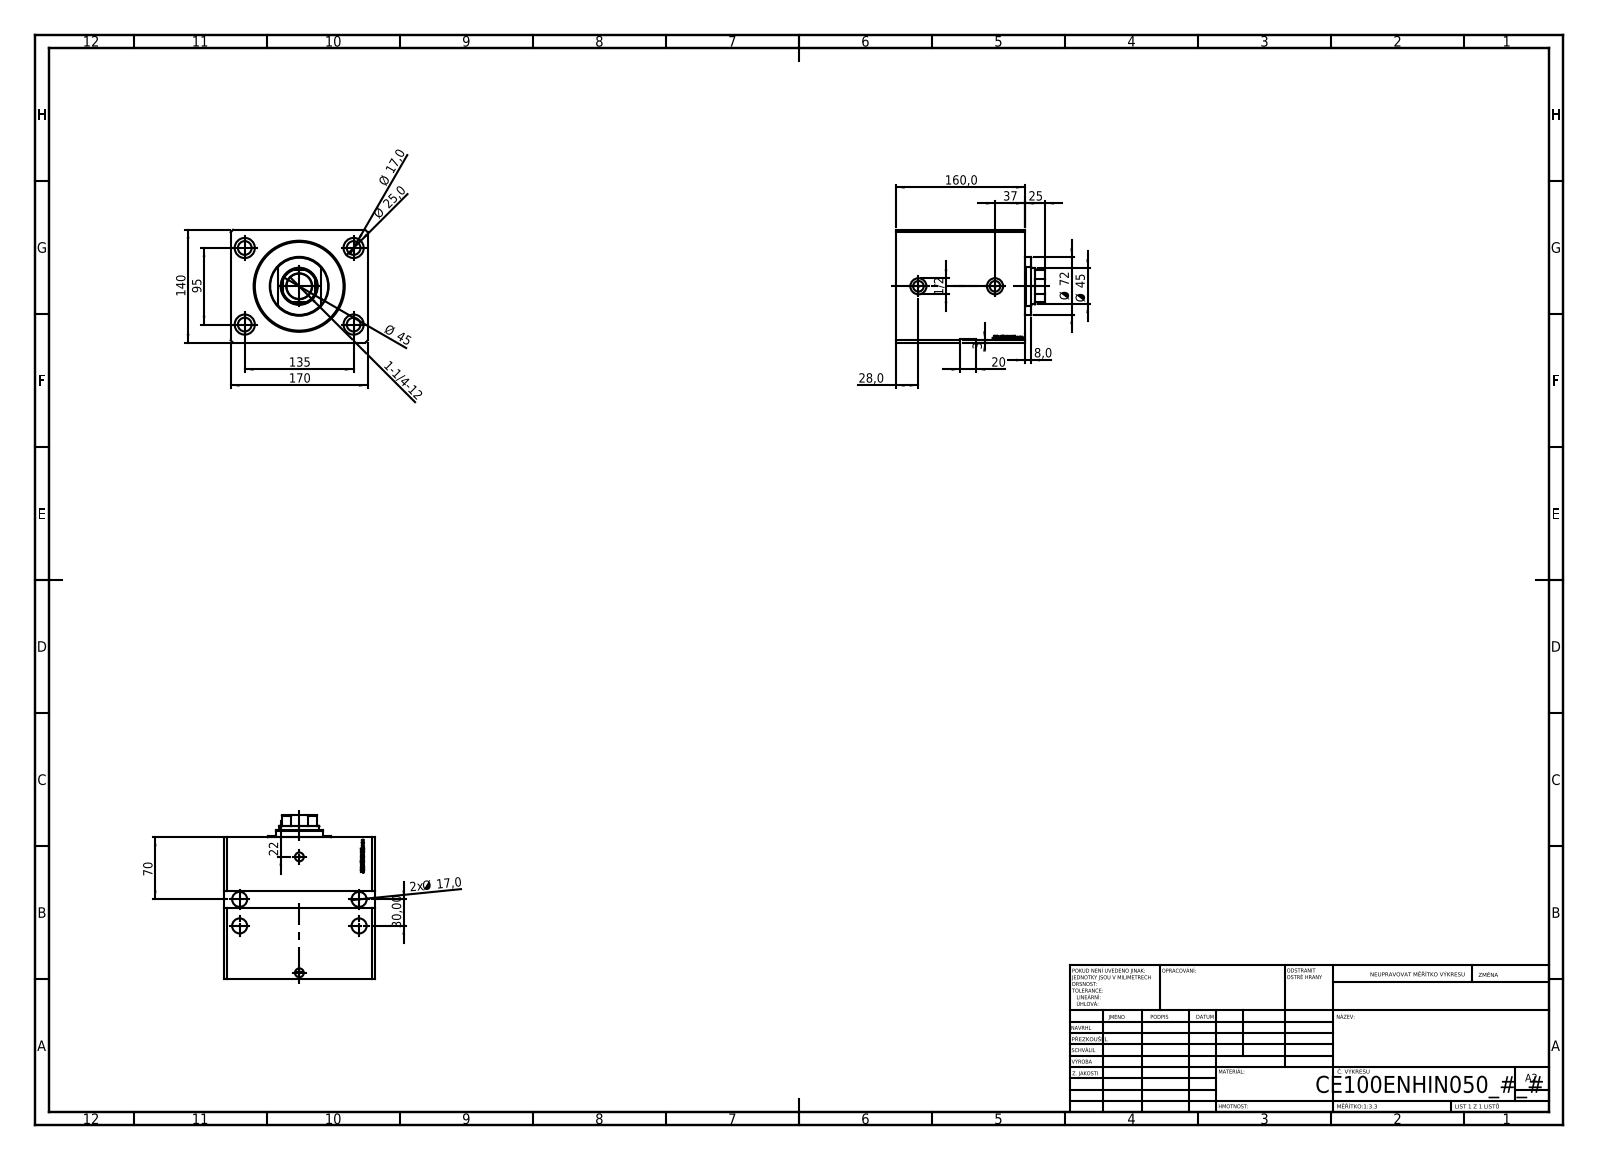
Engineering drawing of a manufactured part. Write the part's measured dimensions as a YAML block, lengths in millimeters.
part_name: "V250CE_E_Body; V250CE_VC_E; V250CE_C_VCP"
step_written_by: "SolidWorks 2019 (CONFIG_CONTROL_DESIGN)"
units: millimeters
bodies: {solids: 3, faces: 953, planar: 471, cylindrical: 96, other: 386}
overall_size: [185, 170, 140]
volume: 3212000
surface_area: 328709
round_holes:
  - {diameter: 17, count: 8}
  - {diameter: 1.25, count: 4}
  - {diameter: 25, count: 4}
  - {diameter: 10, count: 2}
  - {diameter: 13.16, count: 2}
  - {diameter: 20, count: 2}
  - {diameter: 31.5, count: 1}
  - {diameter: 45, count: 1}
  - {diameter: 100, count: 1}
  - {diameter: 113, count: 1}
round_bosses_or_shafts:
  - {diameter: 72, count: 1}
partial_cylinders:
  - {radius: 22, count: 1}
face_to_face_distances: [140, 170, 160, 28.9, 131.1, 135, 25, 106.1, 50, 85]
hole_center_spacings: [82.54, 135, 95, 30, 82.83, 85.49, 85.82, 103.15]
